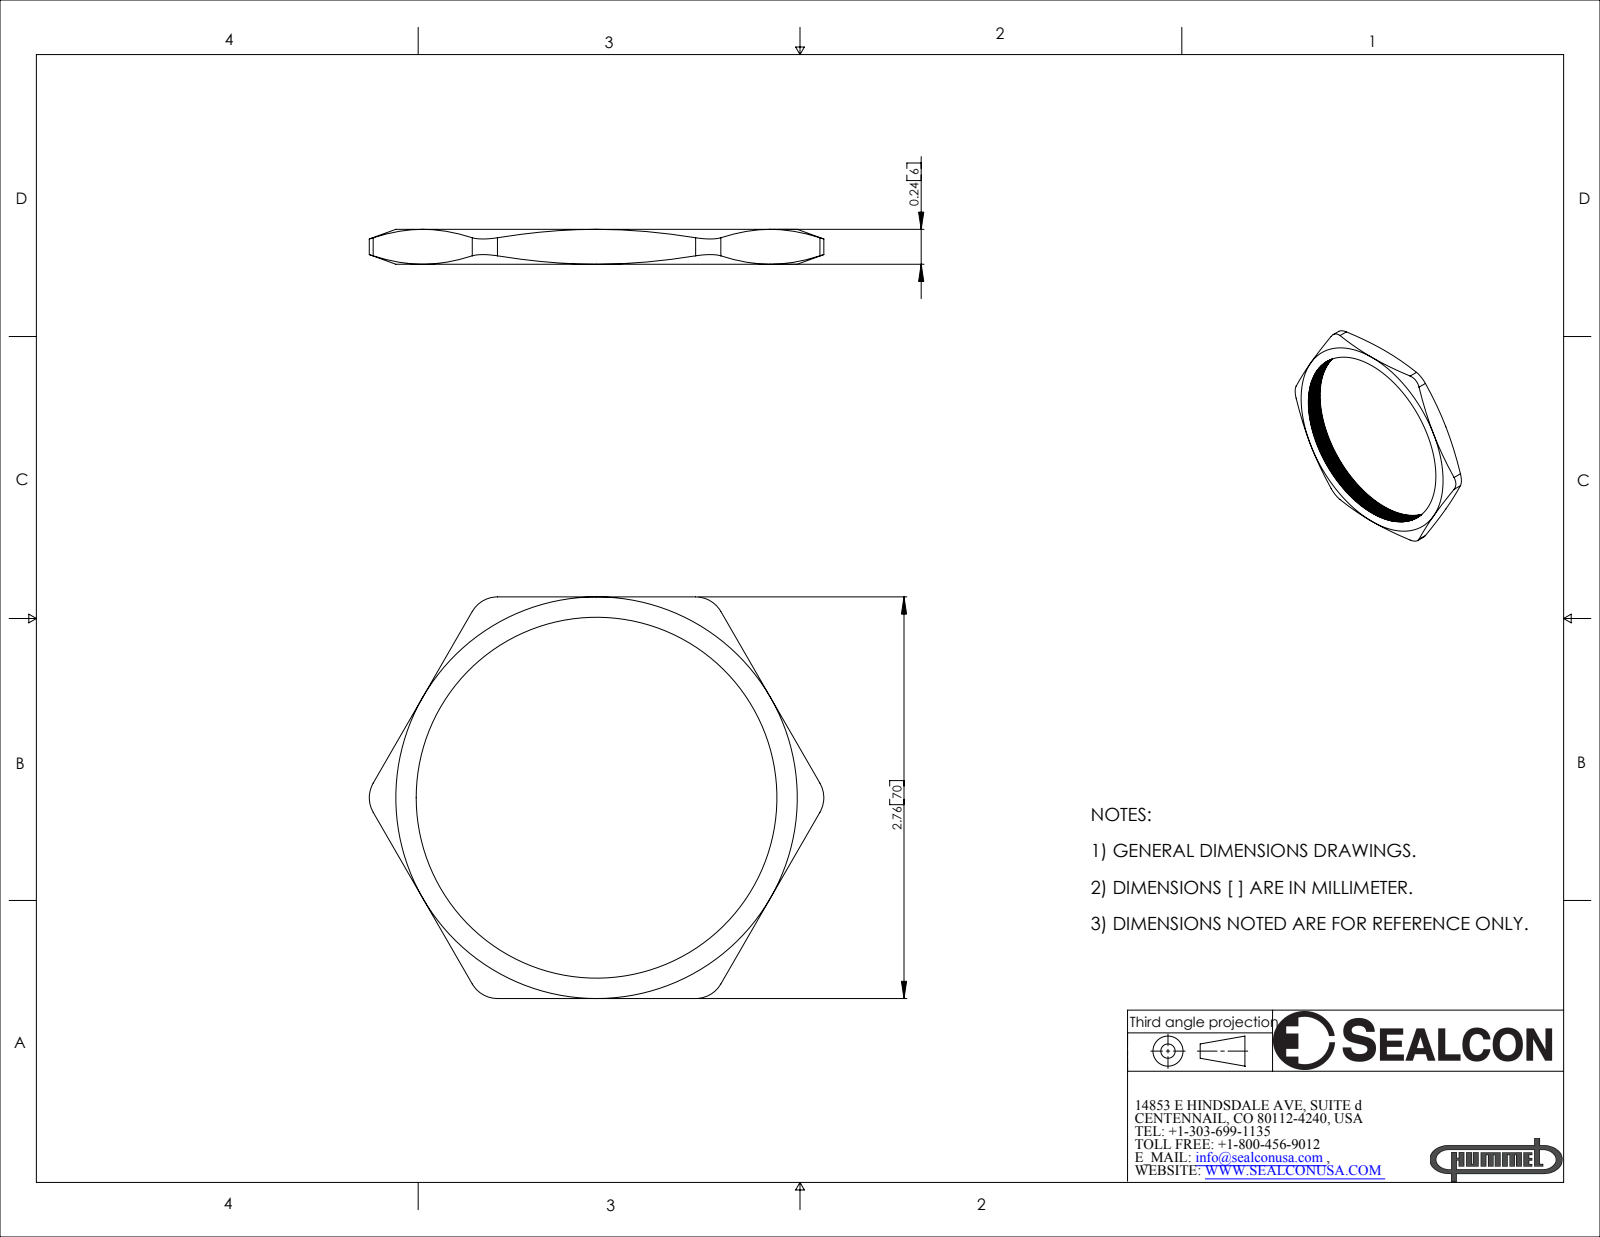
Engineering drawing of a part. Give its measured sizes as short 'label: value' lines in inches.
name: NM-63-BR
written by: SolidWorks 2007 (CONFIG_CONTROL_DESIGN)
unit: in
bodies: 1 solid, 147 faces (8 planar, 7 cylindrical, 132 other)
size: 3.125 × 2.76 × 0.24
volume: 0.372 in³; area: 9.031 in²
rounds: 6× R0.2
face distances: 0.24, 2.76
